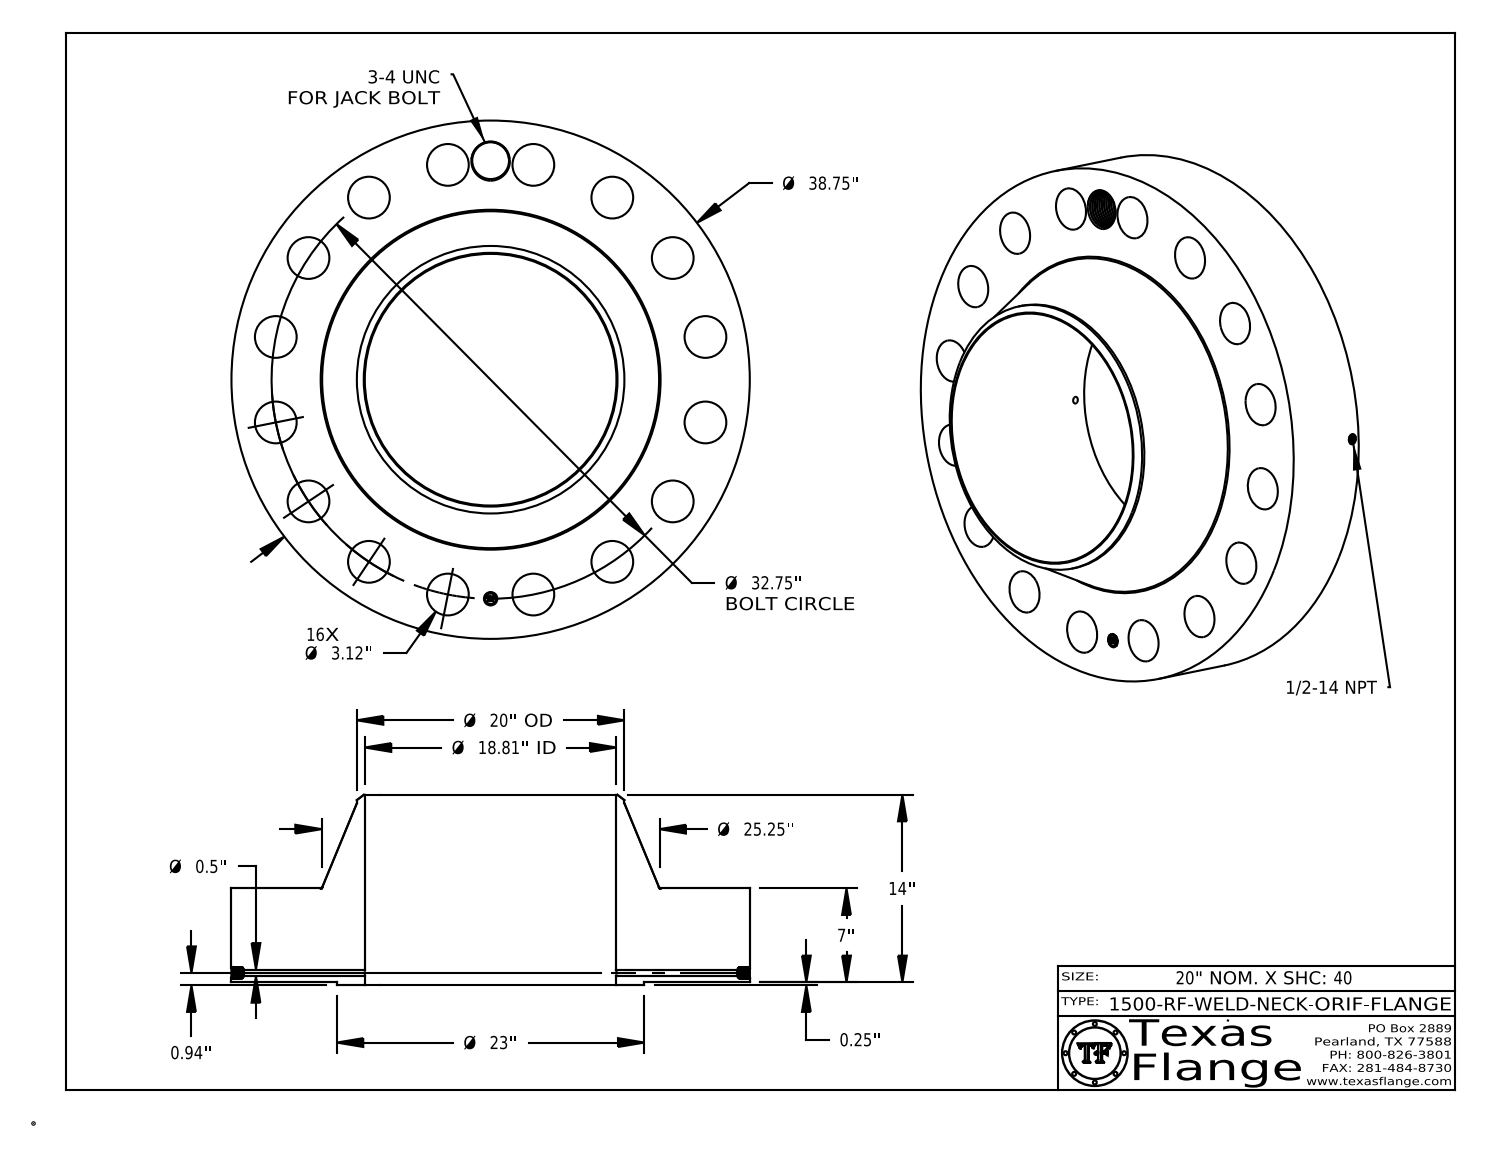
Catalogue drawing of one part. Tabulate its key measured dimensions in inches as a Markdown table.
| quantity | value |
| --- | --- |
| part name | 1500-RF-WELD-NECK |
| STEP written by | CATIA V5 STEP AP214 (AUTOMOTIVE_DESIGN) |
| units | inches |
| bodies | 1 solid, 863 faces (369 planar, 136 cylindrical, 358 other) |
| overall size | 38.75 × 38.75 × 14.25 |
| volume | 6 256 in³ |
| surface area | 4 804 in² |
| round holes (diameter × count) | 3.12 × 16, 0.5 × 1, 0.672 × 1, 1 × 1, 2.75 × 1, 18.812 × 1 |
| round bosses / shafts (diameter × count) | 0.061 × 8, 38.75 × 1, 23 × 1, 20 × 1, 0.788 × 1 |
| main face-to-face distances | 7, 0.25, 7.25, 14.25, 14, 0.015, 7.235, 6.985, 7.015, 0.298 |
| hole center spacings | 30.257, 18.195, 27.231, 32.12, 16.375, 6.389, 6.389, 12.533 |
